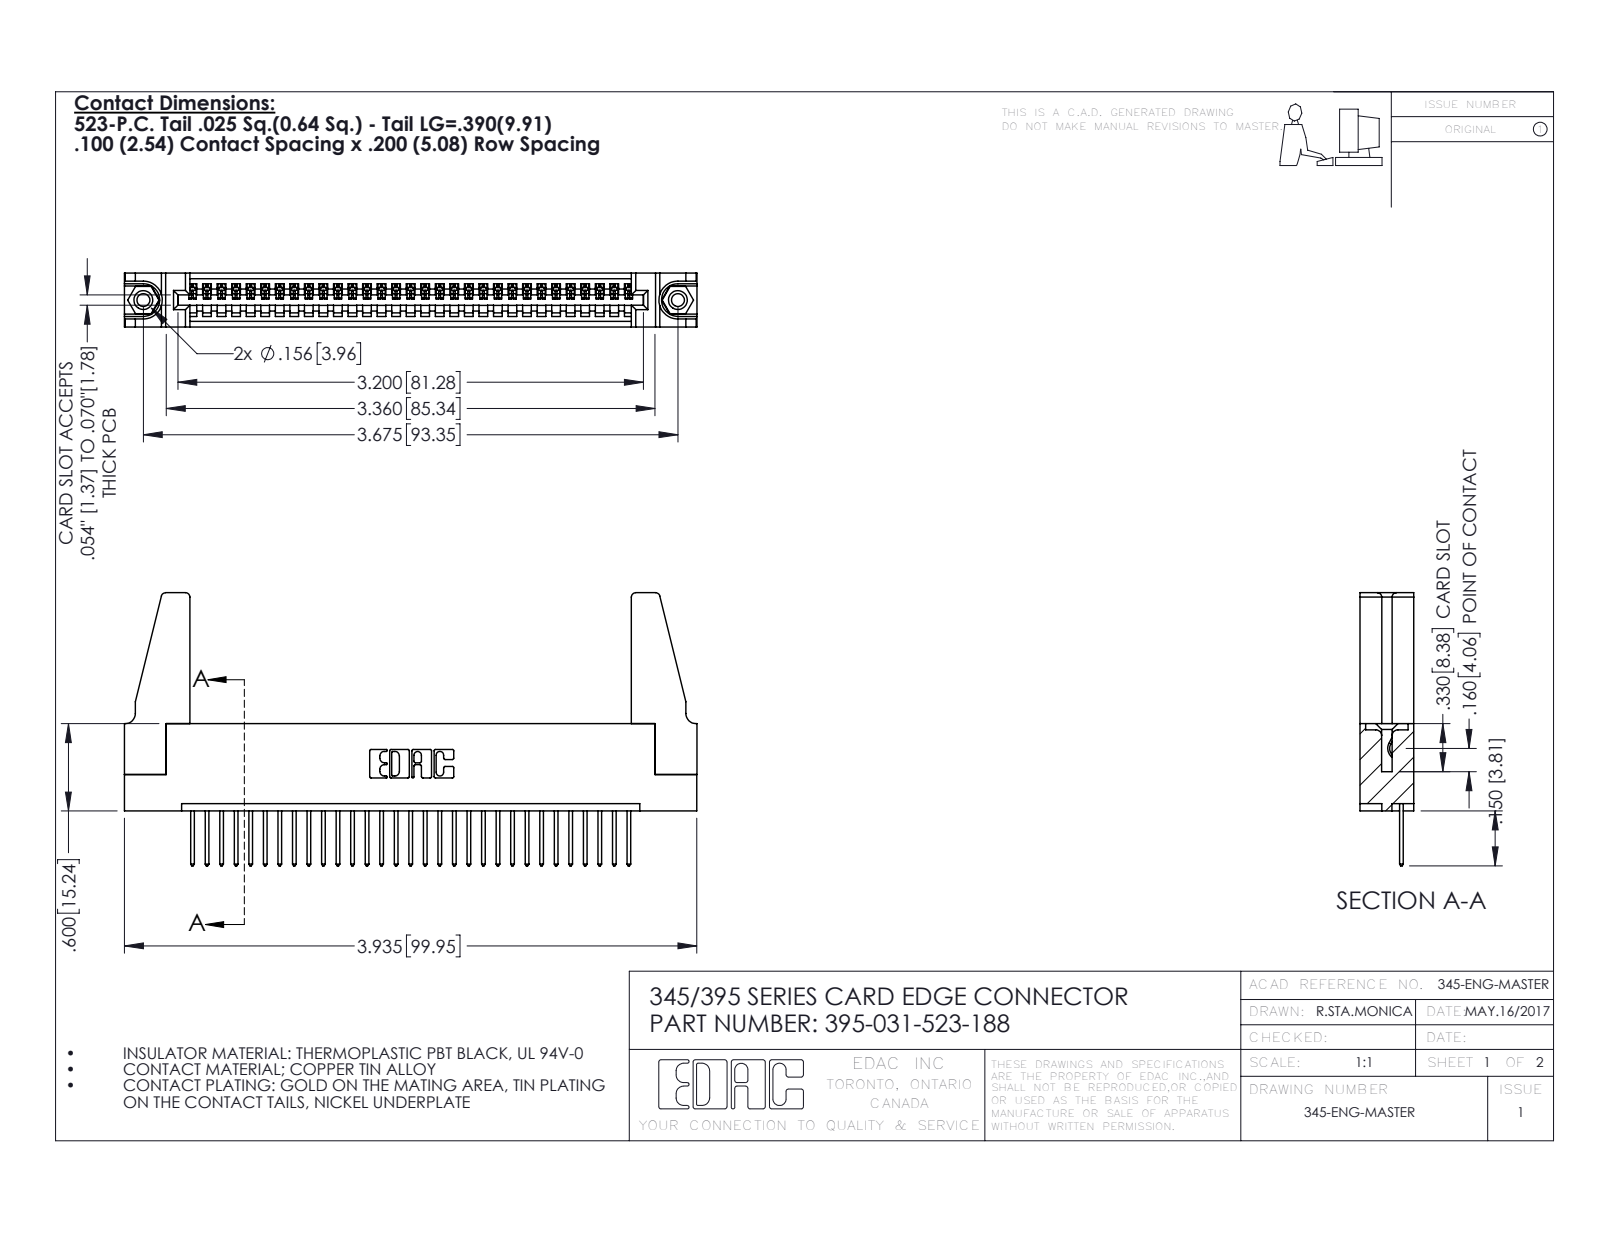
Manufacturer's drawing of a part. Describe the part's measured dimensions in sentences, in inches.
The part is named "395-031-523-188; 345 Part_Flush Mounting Lugs - 0.156 Dia-TH; 345-292-001_345-293-123; 345-220-078_345-220-088 (+1 more)". Its 3-D file was written by "SolidWorks 2016 (CONFIG_CONTROL_DESIGN)". It is 36 solids with 2048 faces: 1392 planar, 640 cylindrical and 16 other. Overall it measures 3.936 by 1.877 by 0.37 inches. Its volume is 0.772 cubic inches and its surface area 24.02 square inches. Round holes: 2 of diameter 0.089, 2 of diameter 0.125, 2 of diameter 0.156, 1 of diameter 0.064. Round bosses or shafts: 2 of diameter 0.155. Partial cylindrical surfaces (rounded edges, fillets, slot ends): 62 of radius 0.006, 62 of radius 0.01, 22 of radius 0.01, 8 of radius 0.03, 6 of radius 0.007, 6 of radius 0.031, 3 of radius 0.026, 2 of radius 0.031. The main face-to-face distances are 0.072, 0.298, 0.37, 0.2, 0.098, 0.272, 0.025, 0.225, 0.149, 0.072. The hole center spacings are 0.27, 3.44, 3.675.
